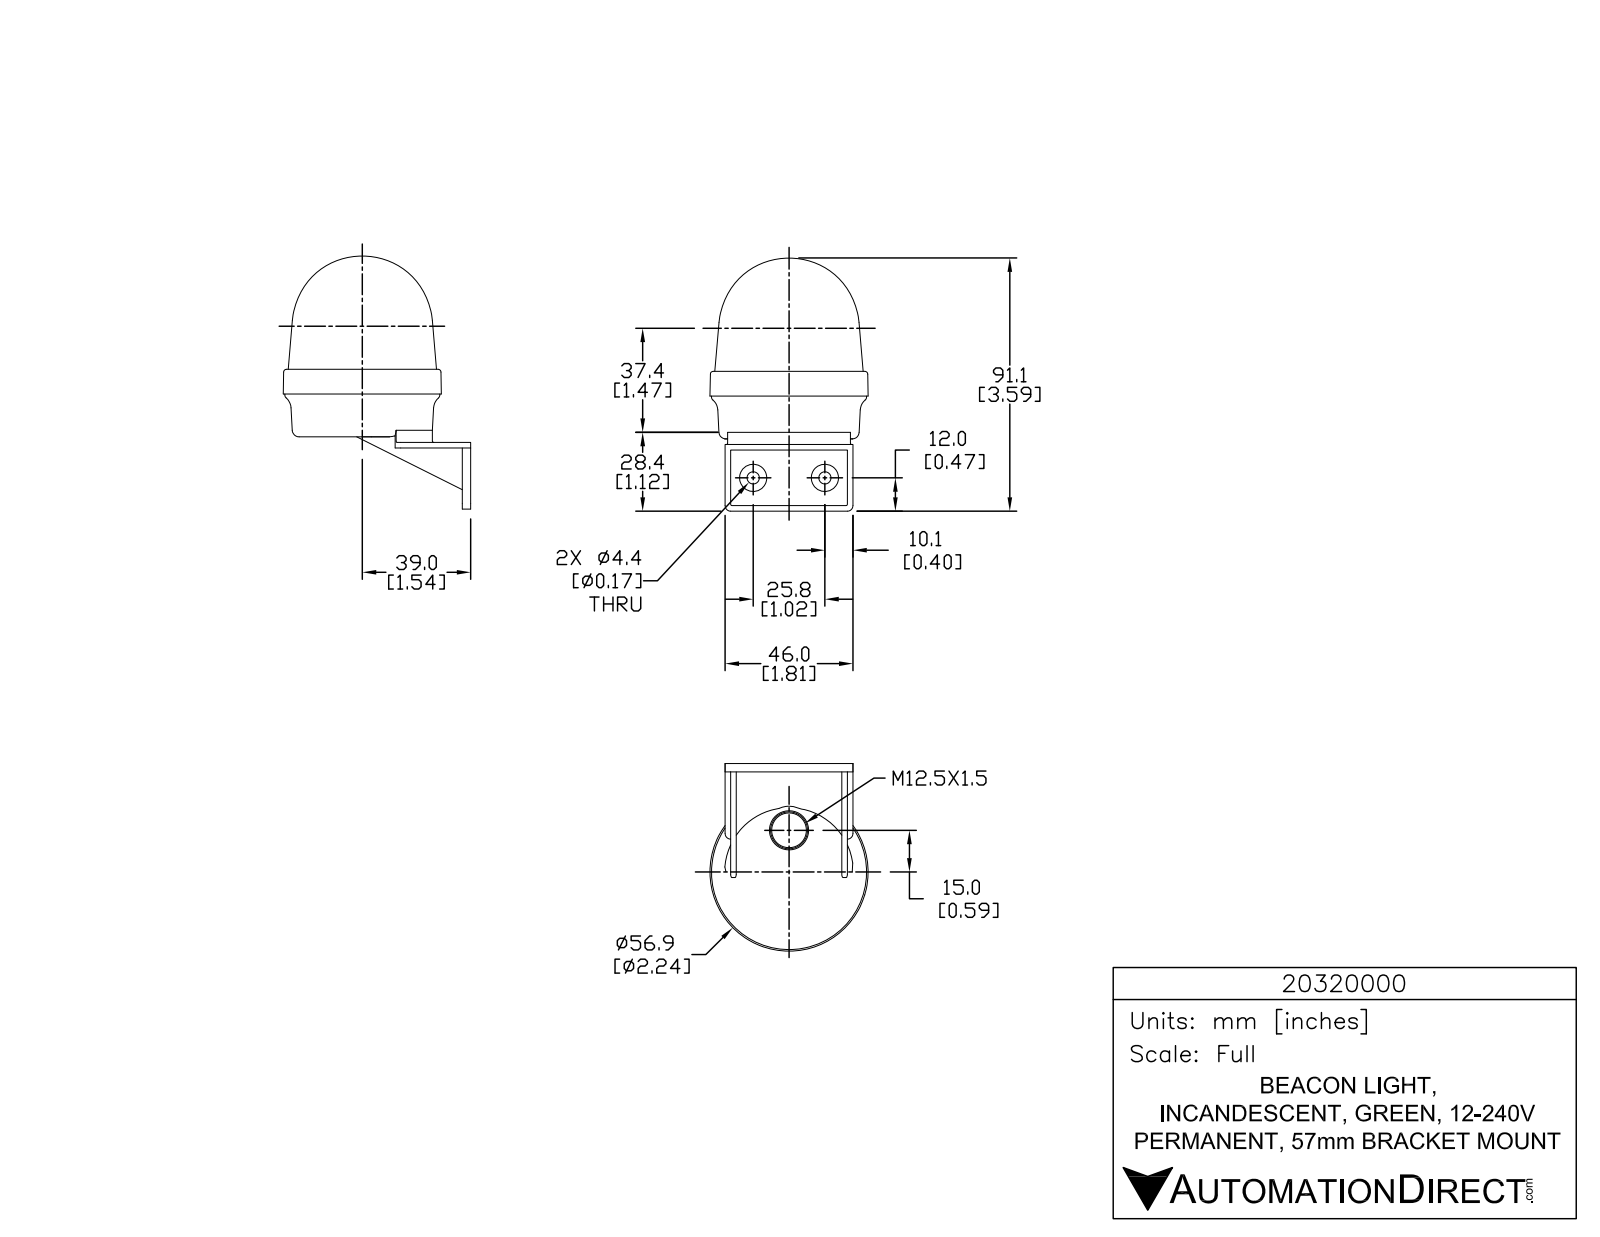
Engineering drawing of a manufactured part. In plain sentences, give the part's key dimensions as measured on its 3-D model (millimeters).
The part is named "20320000". Its 3-D file was written by "SolidWorks 2015 (AUTOMOTIVE_DESIGN)". It is 1 solid with 813 faces: 550 planar, 169 cylindrical and 94 other. Overall it measures 91.1 by 72.07 by 60.76 millimeters. Its volume is 126 840 cubic millimeters and its surface area 18 525 square millimeters. Round holes: 3 of diameter 0.99, 2 of diameter 4.4. Round bosses or shafts: 3 of diameter 5.74, 3 of diameter 1.43, 2 of diameter 9.8, 1 of diameter 55.8. Partial cylindrical surfaces (rounded edges, fillets, slot ends): 6 of radius 0.2, 6 of radius 0.21, 6 of radius 0.21, 6 of radius 0.5, 6 of radius 3.32, 4 of radius 2, 3 of radius 0.1, 3 of radius 0.12. The main face-to-face distances are 2, 4, 40, 42, 1, 3, 38, 22, 24, 44.01. The hole center spacings are 25.8.
